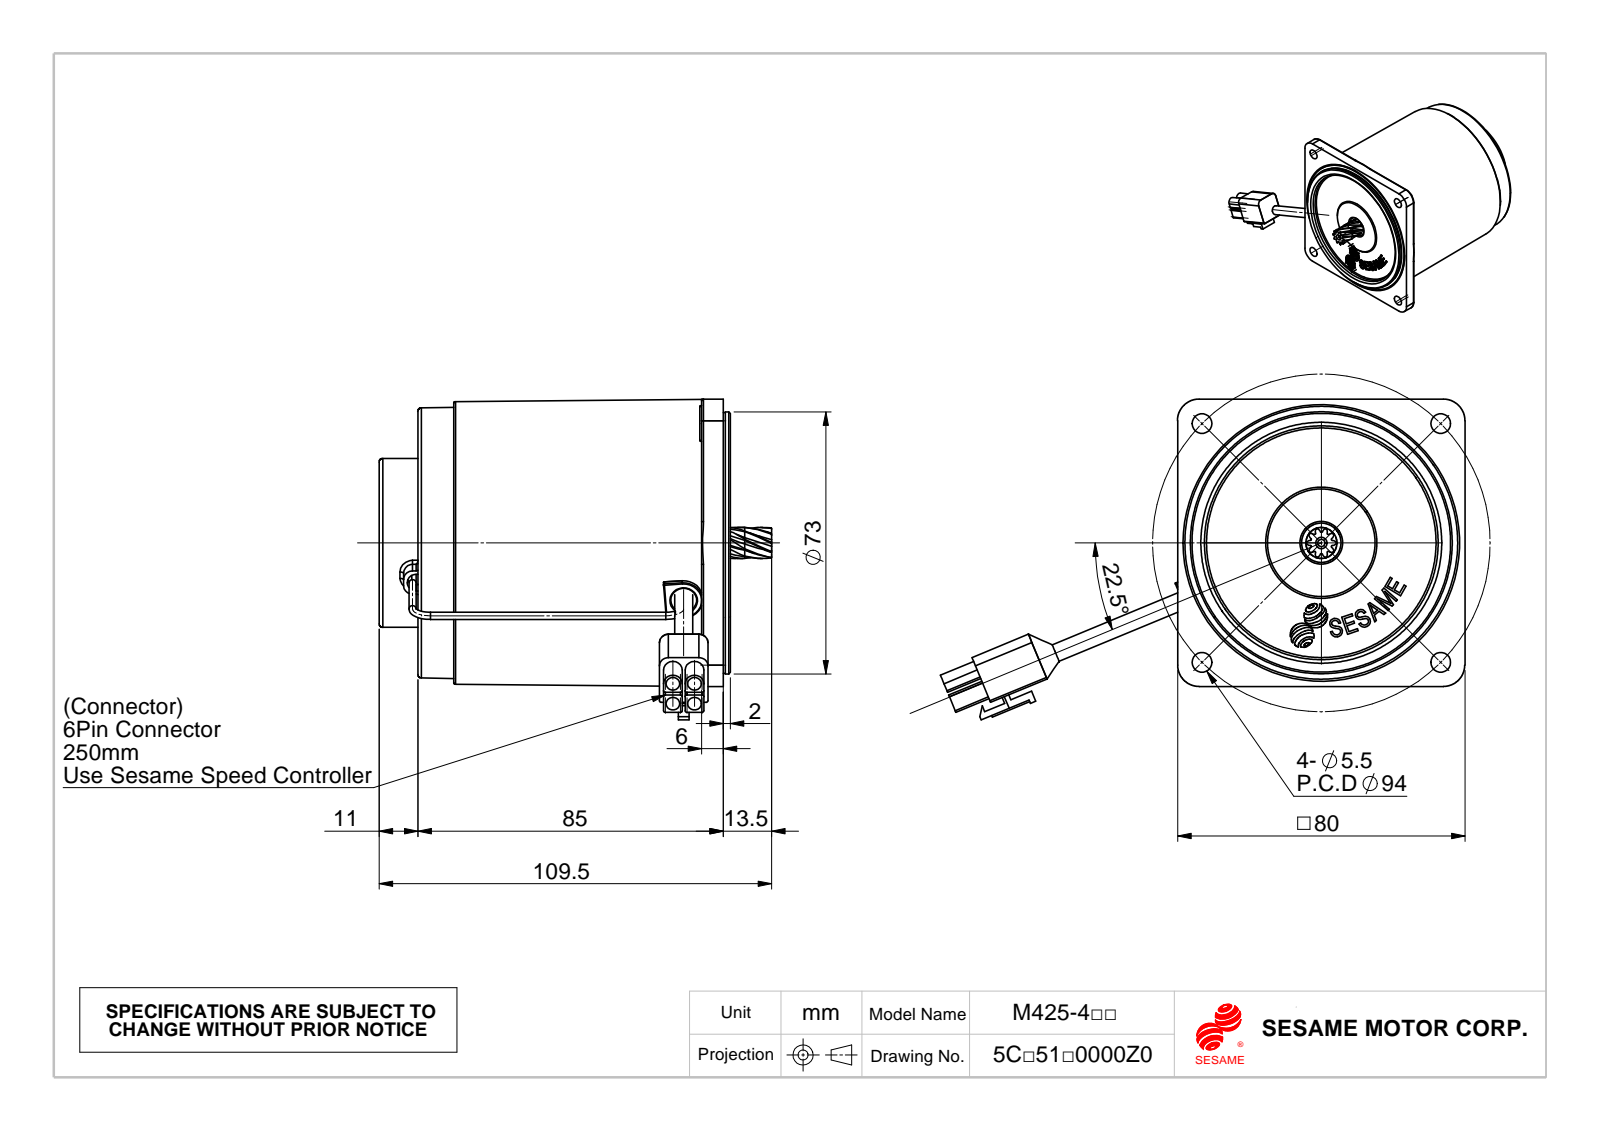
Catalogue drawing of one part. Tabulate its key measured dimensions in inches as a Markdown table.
| quantity | value |
| --- | --- |
| part name | C475-C473_C475成品-車工; 馬達軸25RGN-IK(RK)_0.成品; 發電機下蓋; 6~15W發電機磁鐵組合品 (+5 more) |
| STEP written by | SolidWorks 2010 (CONFIG_CONTROL_DESIGN) |
| units | inches |
| bodies | 23 solids, 1245 faces (396 planar, 557 cylindrical, 292 other) |
| overall size | 5.751 × 4.302 × 3.514 |
| volume | 27.88 in³ |
| surface area | 125.4 in² |
| round holes (diameter × count) | 0.217 × 8, 0.15 × 4, 0.079 × 2, 0.13 × 2, 0.138 × 1, 0.283 × 1, 0.374 × 1, 0.402 × 1, 0.433 × 1, 0.591 × 1, 0.866 × 1, 0.984 × 1 |
| round bosses / shafts (diameter × count) | 0.079 × 2, 2.957 × 1, 2.955 × 1, 2.871 × 1, 2.856 × 1, 2.283 × 1, 1.85 × 1, 1.693 × 1 |
| partial cylindrical surfaces (radius × count) | 0.02 × 18, 0.01 × 8, 0.02 × 8, 0.024 × 8, 0.038 × 8, 0.039 × 8, 0.042 × 8, 0.046 × 8 |
| main face-to-face distances | 0.039, 0.063, 0.02, 3.287, 3.248, 0.087, 3.335, 3.224, 0.047, 0.346 |
| hole center spacings | 0.236, 0.142, 0.167, 2.617, 0.167, 0.197, 0.237, 0.334 |
